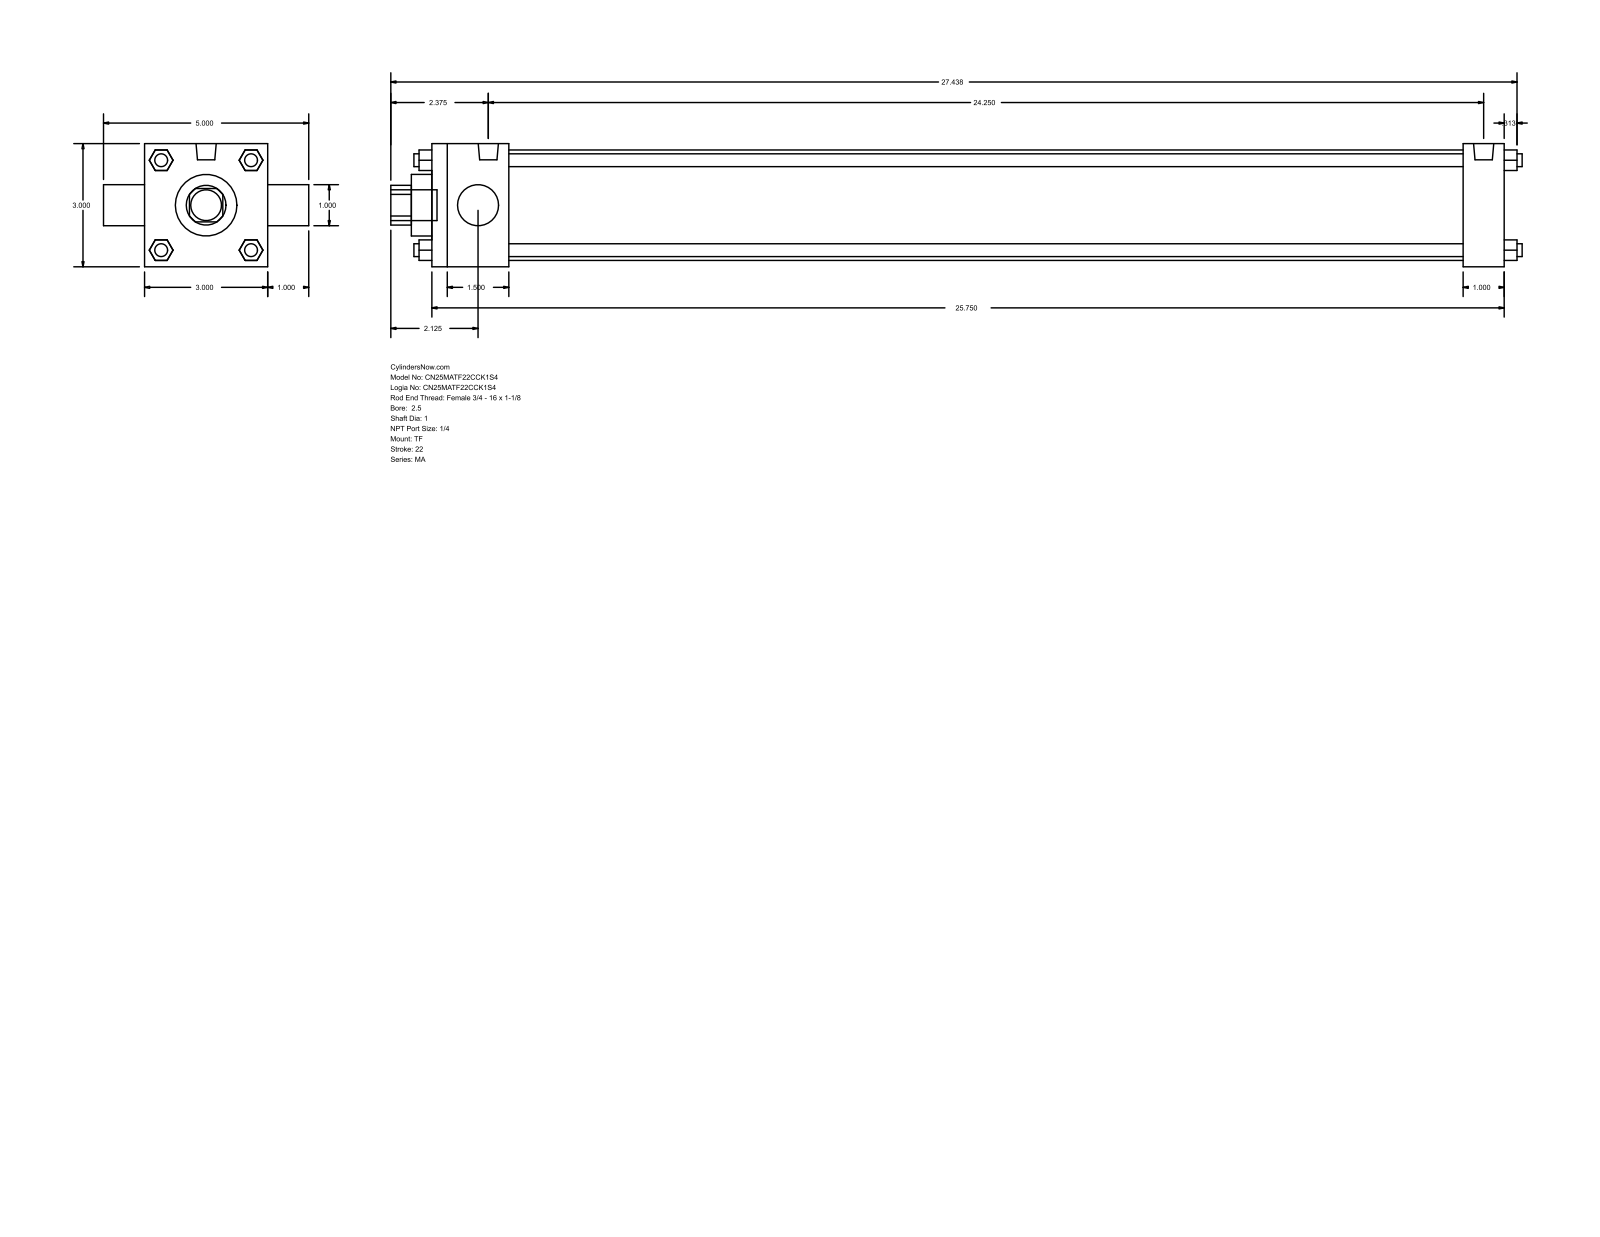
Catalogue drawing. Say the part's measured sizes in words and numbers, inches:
The part is named "MA_TF__0250_1". Its 3-D file was written by "GSSL Pune (CONFIG_CONTROL_DESIGN)". It is 0 solids with 120 faces: 92 planar, 28 cylindrical and 0 other. Overall it measures 27.563 by 5 by 3 inches. Round holes: 2 of diameter 1, 1 of diameter 1.5, 1 of diameter 2.69. Round bosses or shafts: 7 of diameter 0.313, 2 of diameter 0.492, 1 of diameter 0.75. Partial cylindrical surfaces (rounded edges, fillets, slot ends): 1 of radius 0.484. The main face-to-face distances are 3, 26.125, 1, 0.5, 1.875, 25.125, 23.25, 24.25, 4, 1.095.
